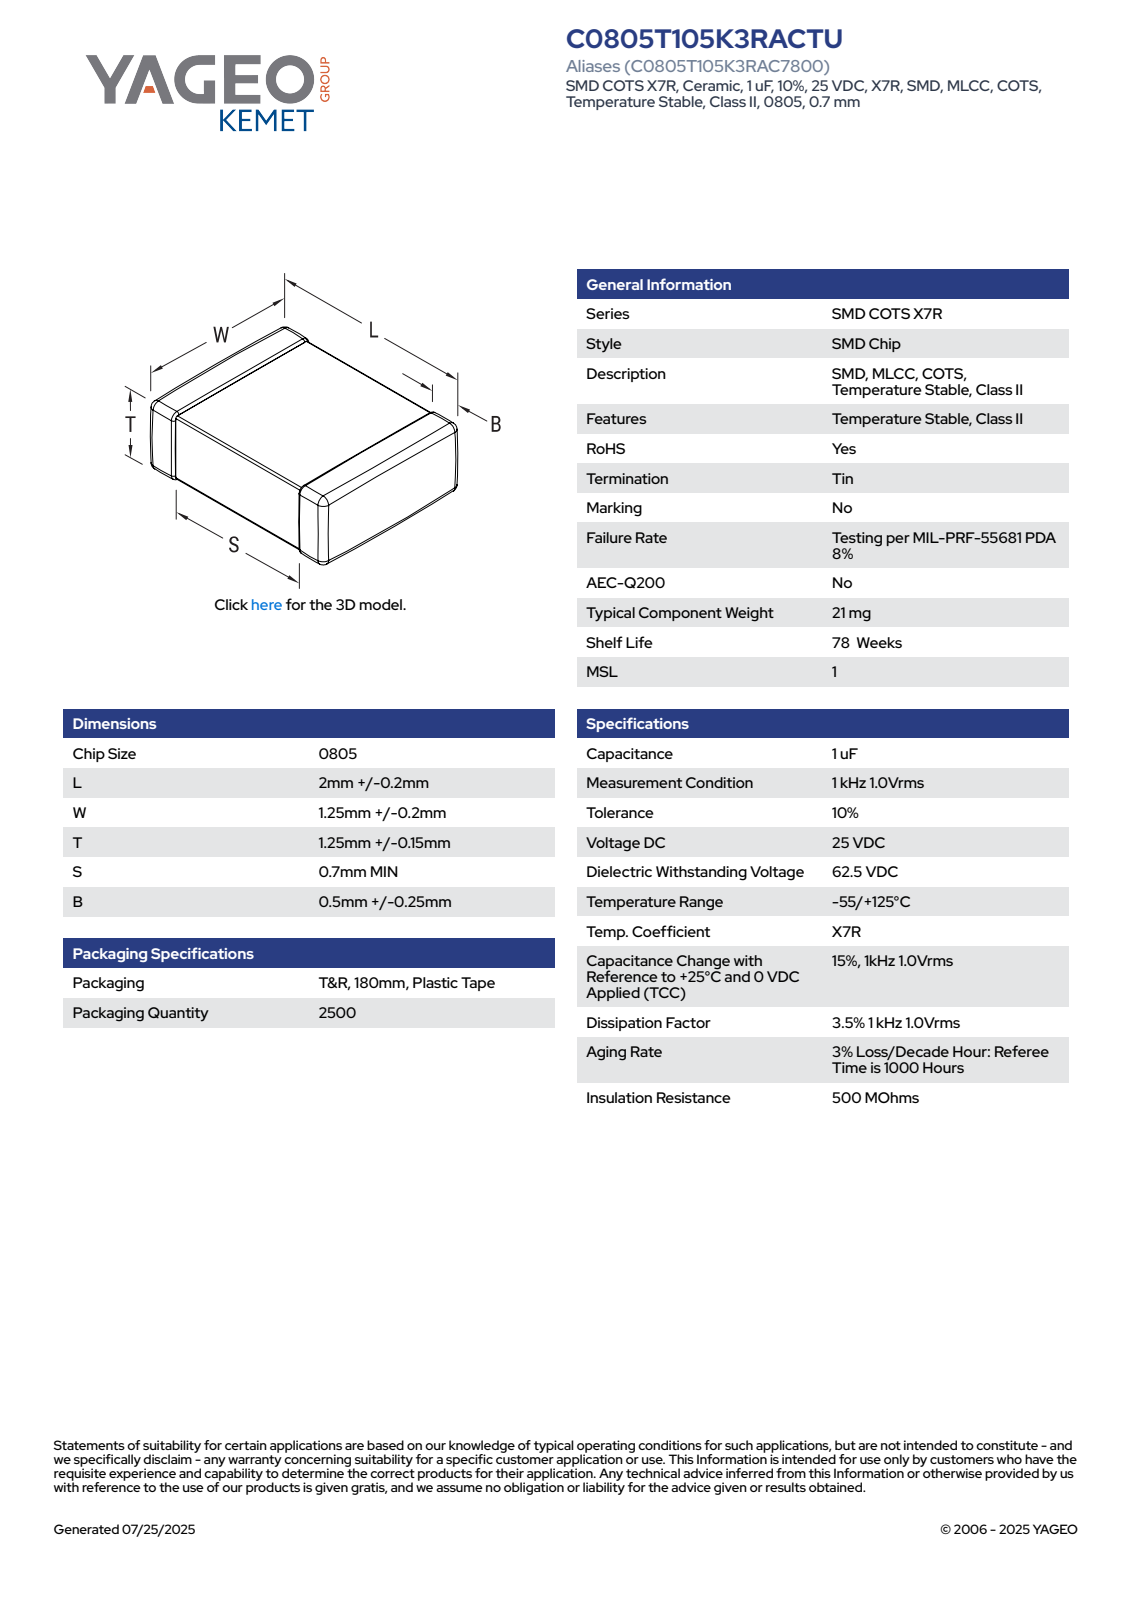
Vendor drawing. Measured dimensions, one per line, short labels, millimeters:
name: CCSM_STD_0805_L2.2W1.45T1.4S1.25B0.75
written by: SolidWorks 2021 (AUTOMOTIVE_DESIGN)
unit: mm
bodies: 4 solids, 121 faces (71 planar, 34 cylindrical, 16 other)
size: 2.2 × 1.45 × 1.4
volume: 4 mm³; area: 17 mm²
face distances: 1.37, 1.4, 2.2, 1.45, 1.42, 1.34, 1.39, 0.97, 1.23, 1.19
